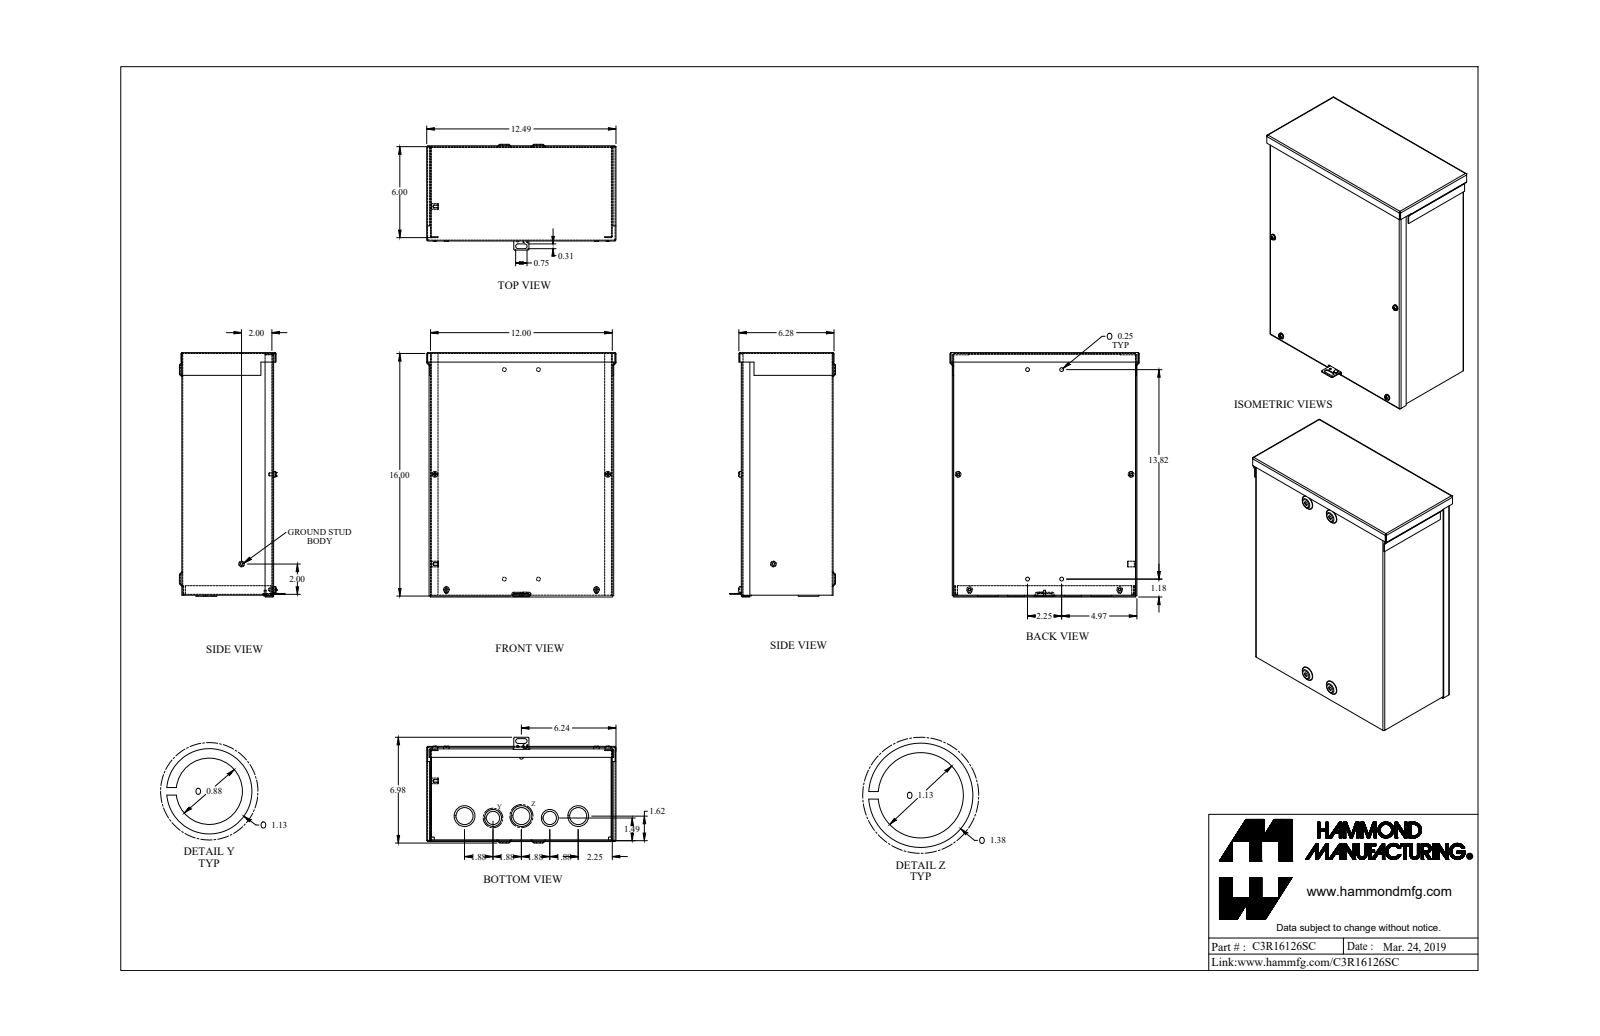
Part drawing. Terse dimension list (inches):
name: C3R16126SC_Default
written by: SolidWorks 2019 (CONFIG_CONTROL_DESIGN)
unit: in
bodies: 11 solids, 429 faces (226 planar, 117 cylindrical, 86 other)
size: 16.12 × 12.489 × 6.977
volume: 46.52 in³; area: 1 642 in²
holes: 4× ⌀0.17, 4× ⌀0.25, 3× ⌀1.125, 2× ⌀0.875, 1× ⌀0.125, 1× ⌀0.137, 1× ⌀0.156
bosses: 4× ⌀0.19, 3× ⌀0.375, 2× ⌀1.375, 2× ⌀1.125, 2× ⌀0.375, 1× ⌀1.375, 1× ⌀0.125
rounds: 21× R0.029, 21× R0.086, 8× R0.109, 8× R0.125, 2× R0.156
face distances: 0.057, 6, 5.943, 6.057, 11.943, 0.057, 12, 11.886, 15.886, 15.943
hole spacings: 8.291, 9.717, 3.75, 1.879, 1.88, 2.25, 3.92, 5.396
